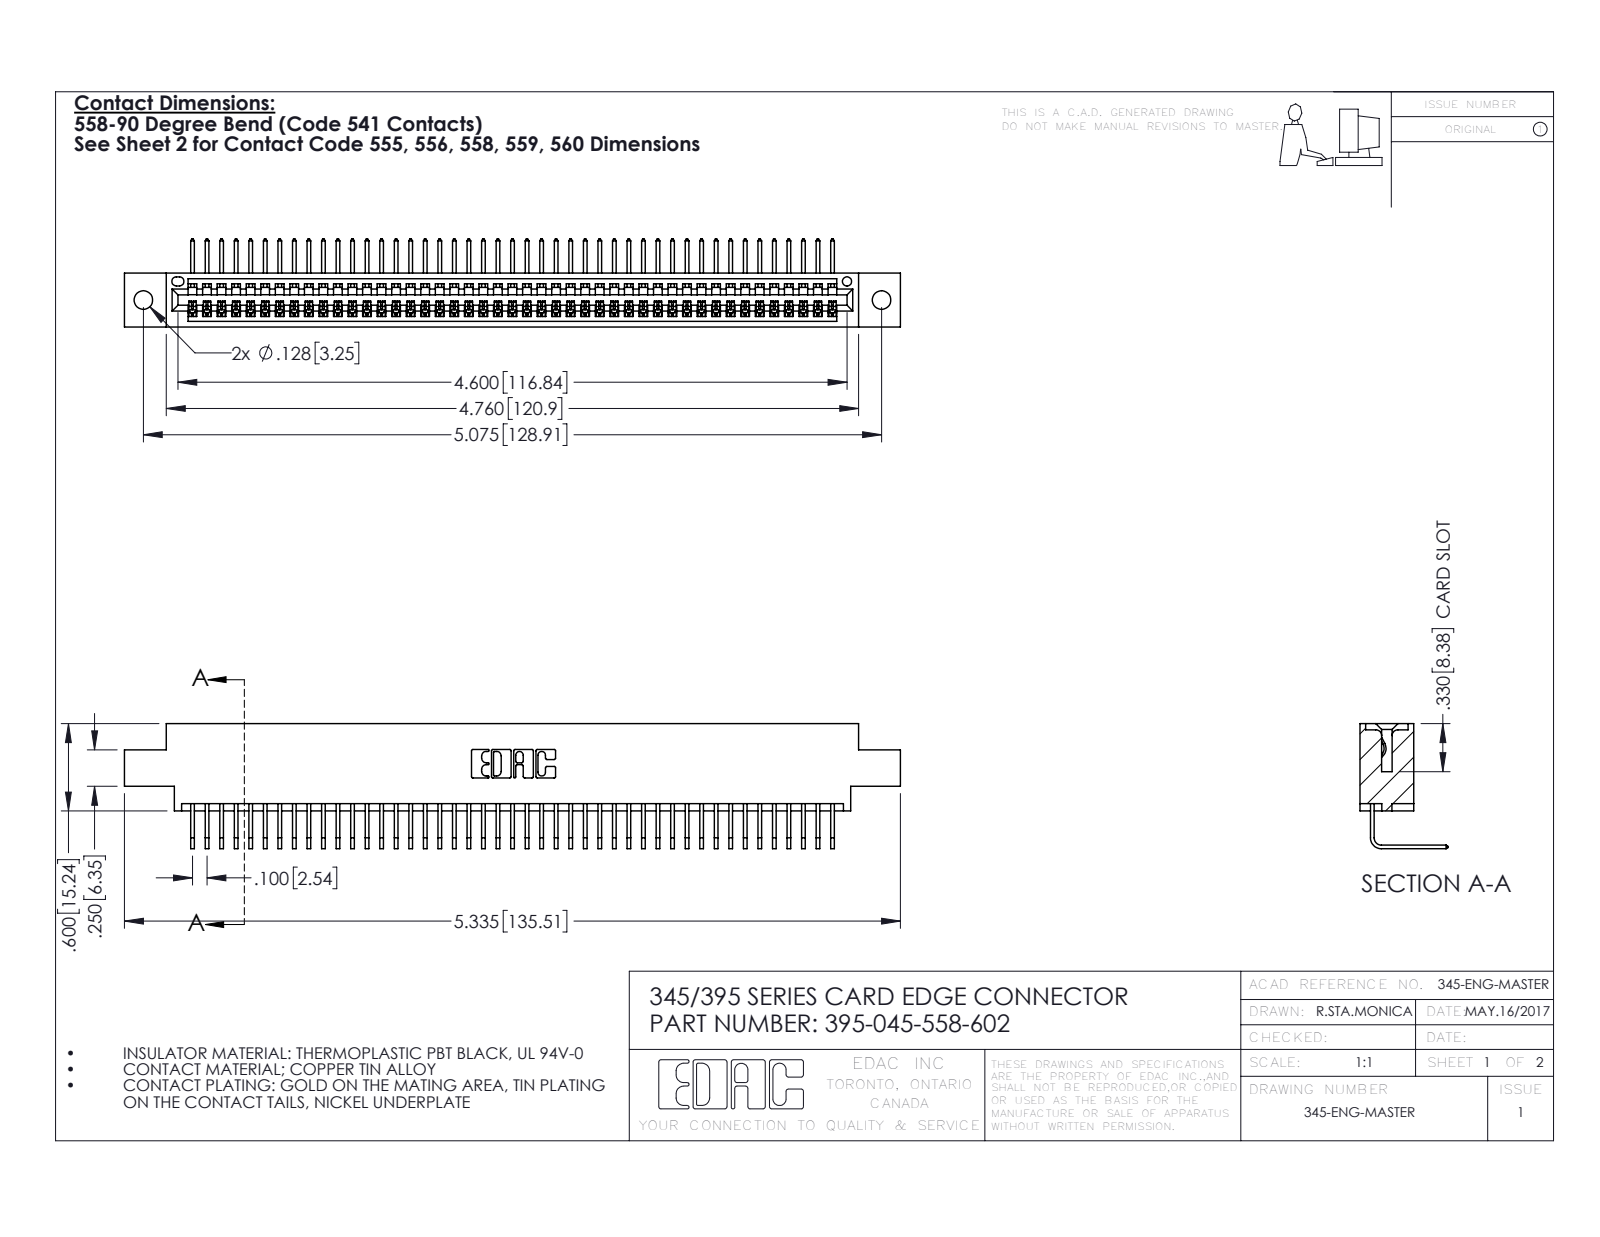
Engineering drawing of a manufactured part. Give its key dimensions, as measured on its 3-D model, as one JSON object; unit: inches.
{"part_name": "395-045-558-602; 345-292-001_558 Tail - 2; 345 Part_0.170 Offset - 0.128 Dia", "step_written_by": "SolidWorks 2016 (CONFIG_CONTROL_DESIGN)", "units": "inches", "bodies": {"solids": 46, "faces": 2830, "planar": 1974, "cylindrical": 856, "other": 0}, "overall_size": [5.335, 0.859, 0.605], "volume_in3": 0.787, "surface_area_in2": 27.77, "round_holes": [[0.128, 2], [0.064, 1]], "partial_cylinders_radius": [[0.006, 90], [0.01, 22], [0.007, 6], [0.031, 6], [0.026, 3], [0.031, 2], [0.04, 2], [0.014, 1]], "face_to_face_distances": [0.072, 0.298, 0.37, 0.2, 0.098, 0.272, 0.025, 0.225, 0.175, 0.149], "hole_center_spacings": [0.27, 4.839, 5.075]}
